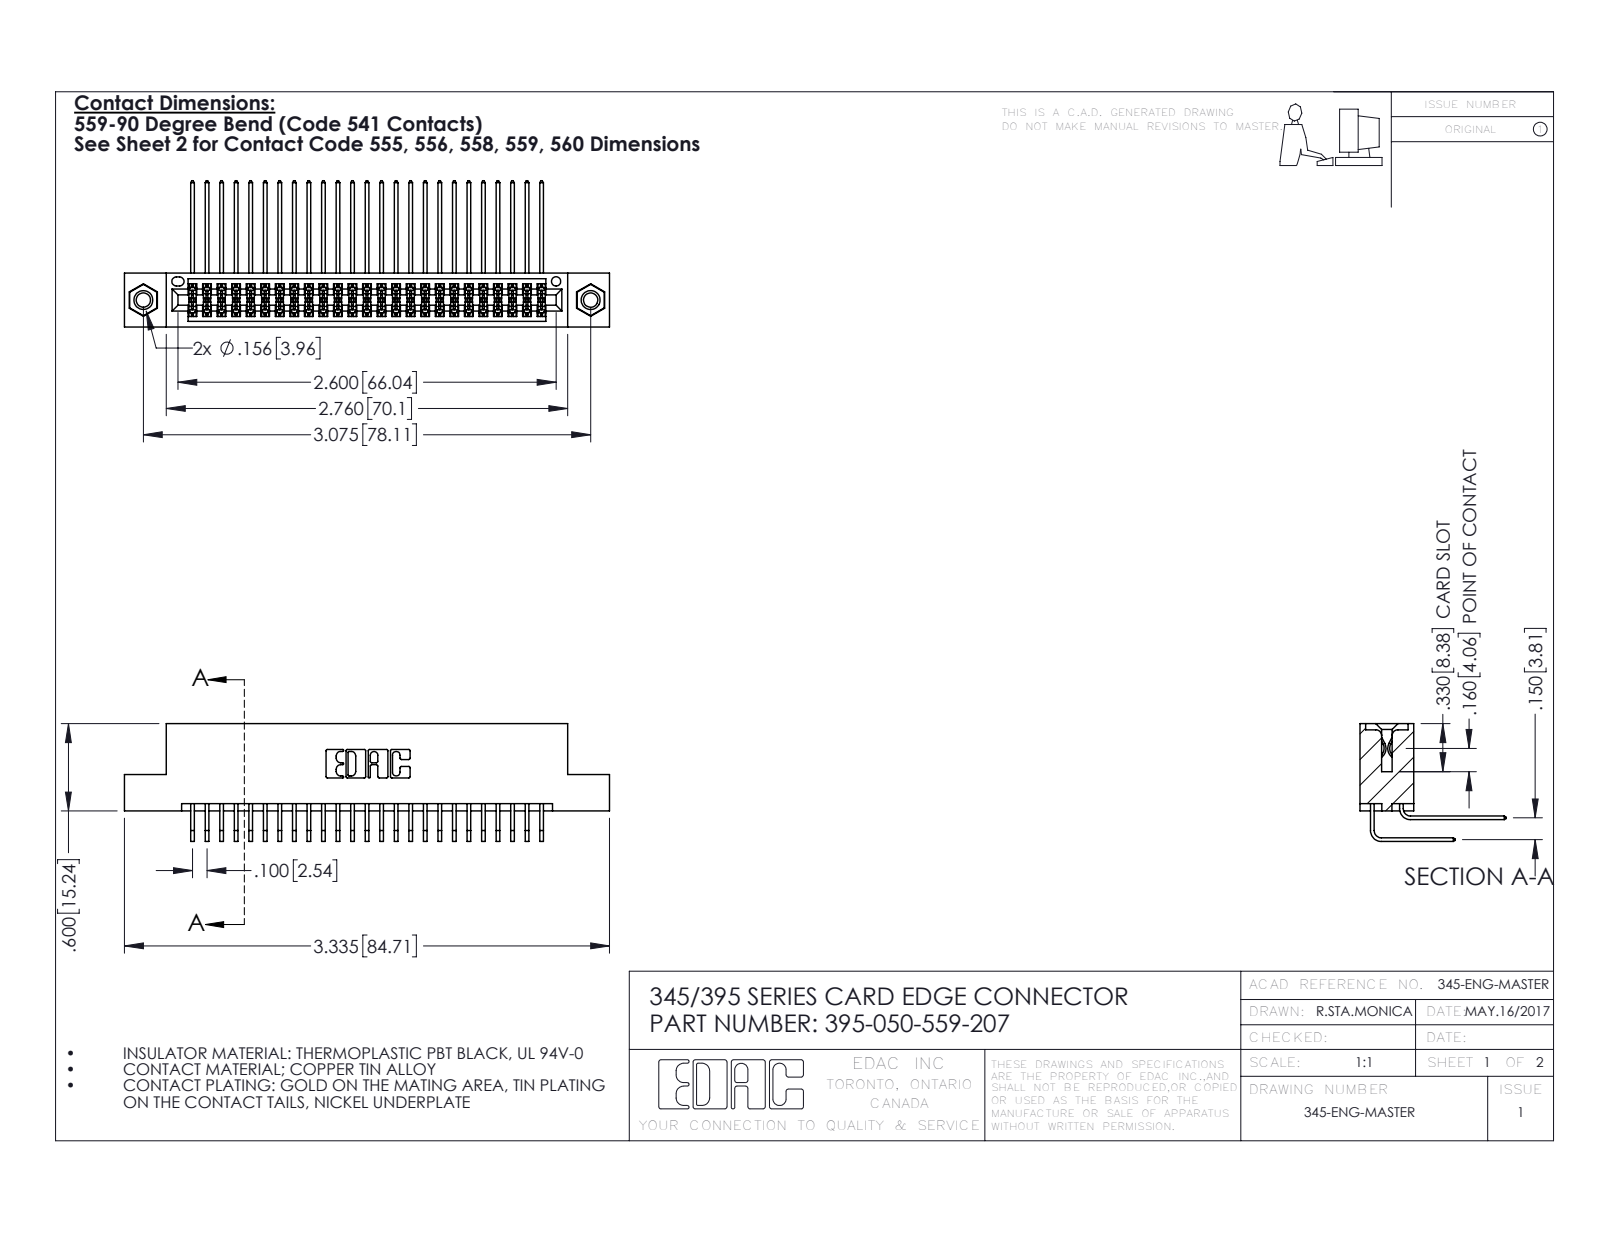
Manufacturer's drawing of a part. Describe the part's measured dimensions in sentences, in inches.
The part is named "345-292-001_559 Tail - 2; 345 Part_Flush Mounting Lugs - 0.156 Dia-TI; 345-292-001_558 559 Tail - 1; 395-050-559-207 (+1 more)". Its 3-D file was written by "SolidWorks 2016 (CONFIG_CONTROL_DESIGN)". It is 53 solids with 2786 faces: 1862 planar, 908 cylindrical and 16 other. Overall it measures 3.335 by 1.005 by 0.809 inches. Its volume is 0.509 cubic inches and its surface area 20.76 square inches. Round holes: 2 of diameter 0.098, 2 of diameter 0.125, 2 of diameter 0.156, 1 of diameter 0.064. Round bosses or shafts: 2 of diameter 0.155. Partial cylindrical surfaces (rounded edges, fillets, slot ends): 75 of radius 0.006, 22 of radius 0.01, 6 of radius 0.007, 6 of radius 0.031, 3 of radius 0.026, 2 of radius 0.014, 2 of radius 0.019, 2 of radius 0.022. The main face-to-face distances are 0.072, 0.298, 0.2, 0.37, 0.098, 0.272, 0.025, 0.225, 0.15, 0.175. The hole center spacings are 0.27, 2.84, 3.075.
